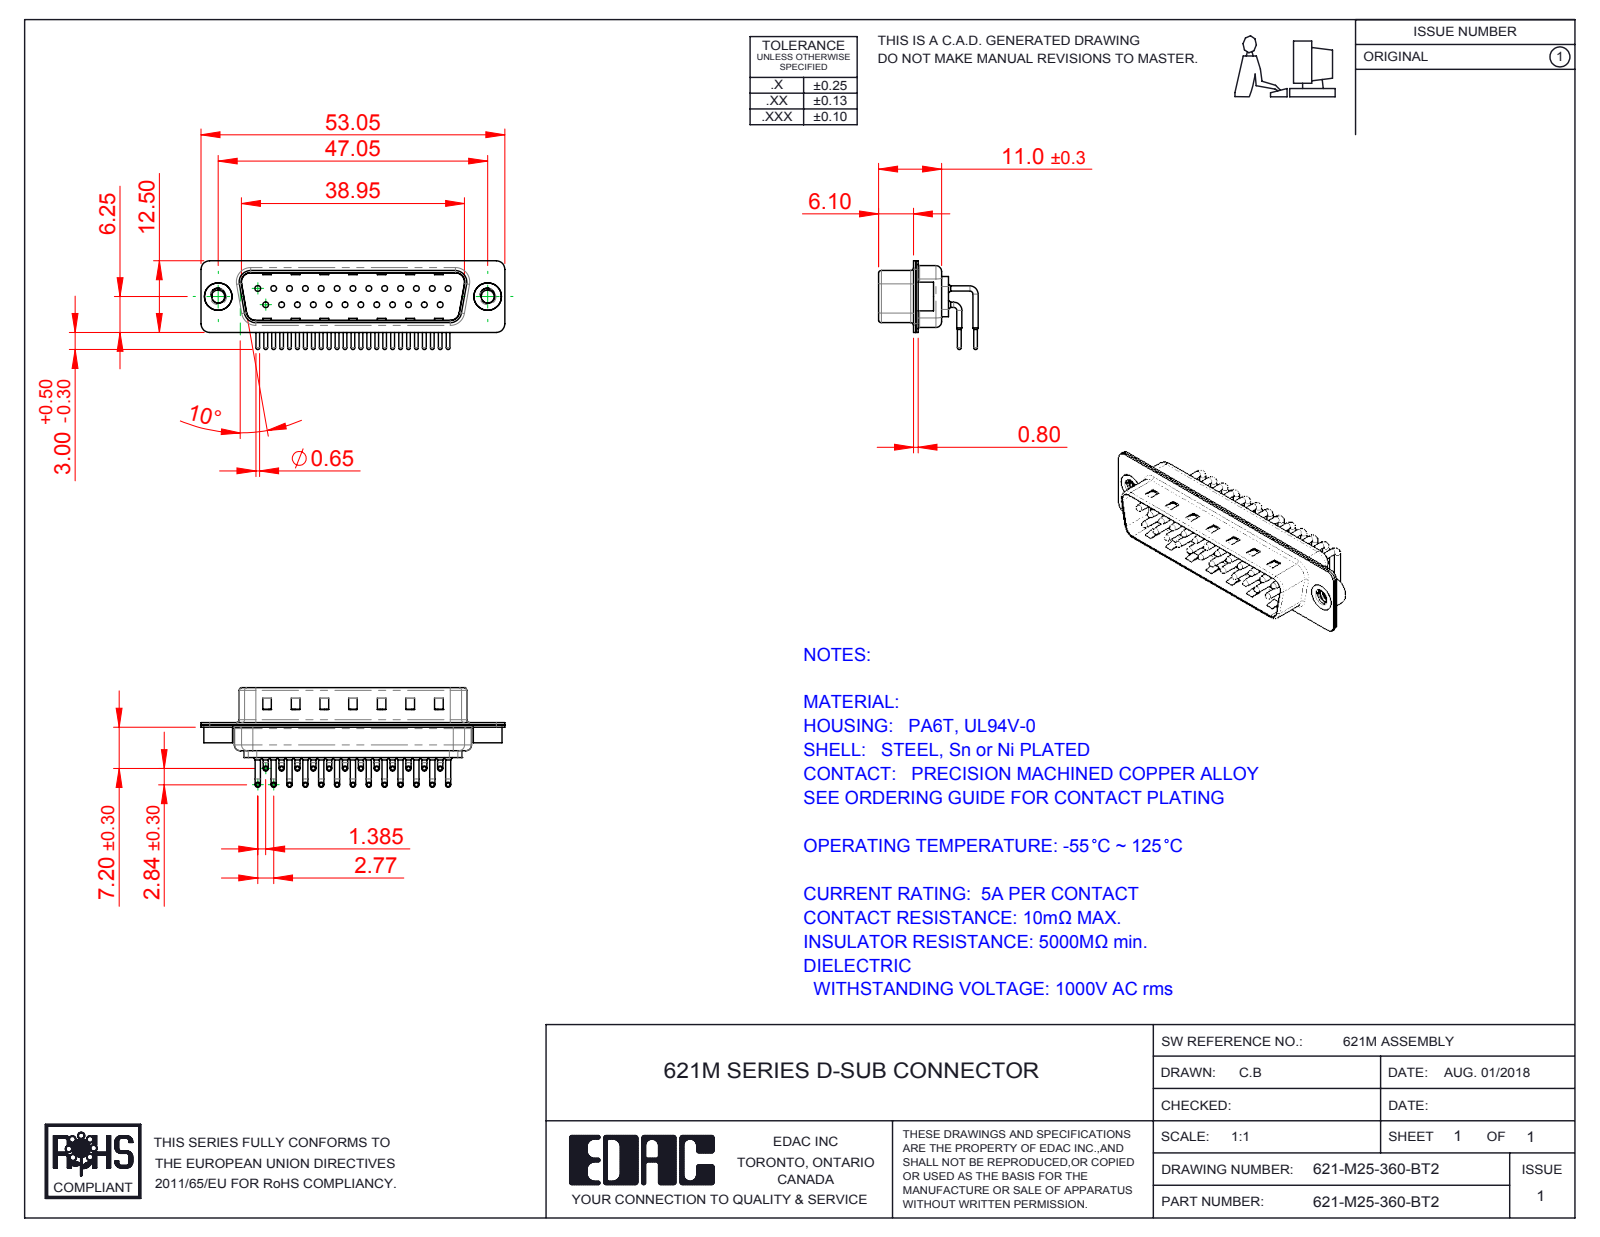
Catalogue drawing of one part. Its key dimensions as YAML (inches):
part_name: "621M Contact Row 1; 621M Shell Front_25 Contacts; 621M Housing_25 Contacts; 621M Contact Row 2 (+3 more)"
step_written_by: "SolidWorks 2016 (CONFIG_CONTROL_DESIGN)"
units: inches
bodies: {solids: 30, faces: 3126, planar: 1771, cylindrical: 1037, other: 318}
overall_size: [2.089, 0.685, 0.61]
volume: 0.175
surface_area: 11.76
round_holes:
  - {diameter: 0.039, count: 25}
  - {diameter: 0.067, count: 25}
  - {diameter: 0.079, count: 25}
  - {diameter: 0.089, count: 2}
  - {diameter: 0.157, count: 2}
  - {diameter: 0.189, count: 2}
round_bosses_or_shafts:
  - {diameter: 0.035, count: 50}
  - {diameter: 0.059, count: 25}
  - {diameter: 0.026, count: 25}
  - {diameter: 0.197, count: 2}
  - {diameter: 0.193, count: 2}
partial_cylinders:
  - {radius: 0.04, count: 25}
  - {radius: 0.059, count: 16}
  - {radius: 0.079, count: 12}
  - {radius: 0.02, count: 8}
  - {radius: 0.063, count: 8}
  - {radius: 0.01, count: 4}
  - {radius: 0.024, count: 4}
  - {radius: 0.026, count: 4}
face_to_face_distances: [0.016, 0.033, 0.376, 0.343, 0.049, 0.409, 0.059, 0.075, 0.014, 0.24]
hole_center_spacings: [0.124, 0.327, 0.109, 0.218, 0.436, 0.654, 0.198, 0.198]
